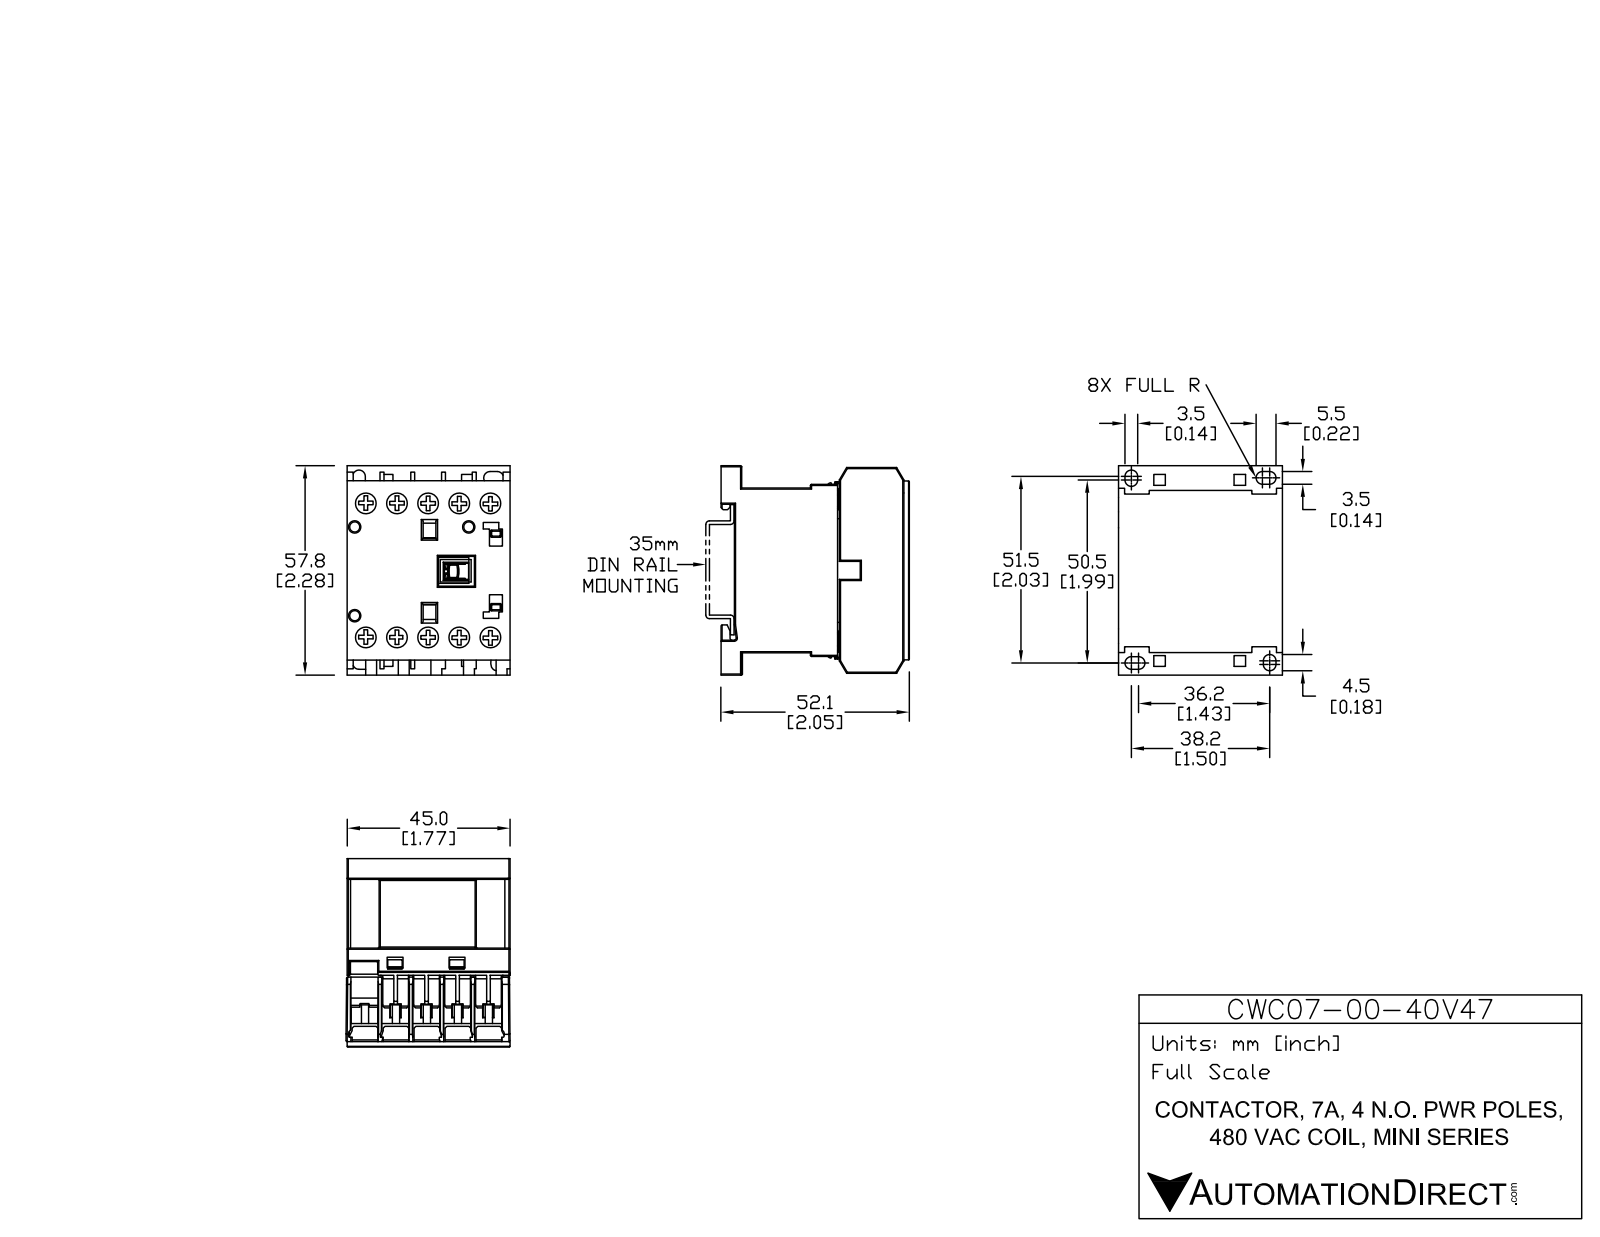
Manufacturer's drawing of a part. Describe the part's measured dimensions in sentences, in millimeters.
The part is named "CWC07-00-40V47". Its 3-D file was written by "SolidWorks 2013 (AUTOMOTIVE_DESIGN)". It is 15 solids with 535 faces: 445 planar, 90 cylindrical and 0 other. Overall it measures 58.04 by 52.12 by 45.75 millimeters. Its volume is 97 133 cubic millimeters and its surface area 30 437 square millimeters. Round holes: 10 of diameter 6.2, 3 of diameter 2.8. Round bosses or shafts: 10 of diameter 5.9. Partial cylindrical surfaces (rounded edges, fillets, slot ends): 20 of radius 0.3, 6 of radius 1.72, 2 of radius 1.73, 1 of radius 0.32, 1 of radius 0.42, 1 of radius 0.55. The main face-to-face distances are 8.25, 45.5, 1.25, 16.5, 9.5, 5.5, 17.75, 5.13, 10.63, 7. The hole center spacings are 8.55, 37.94, 17.1, 40.72, 36.96, 25.65, 44.99, 6.91.
